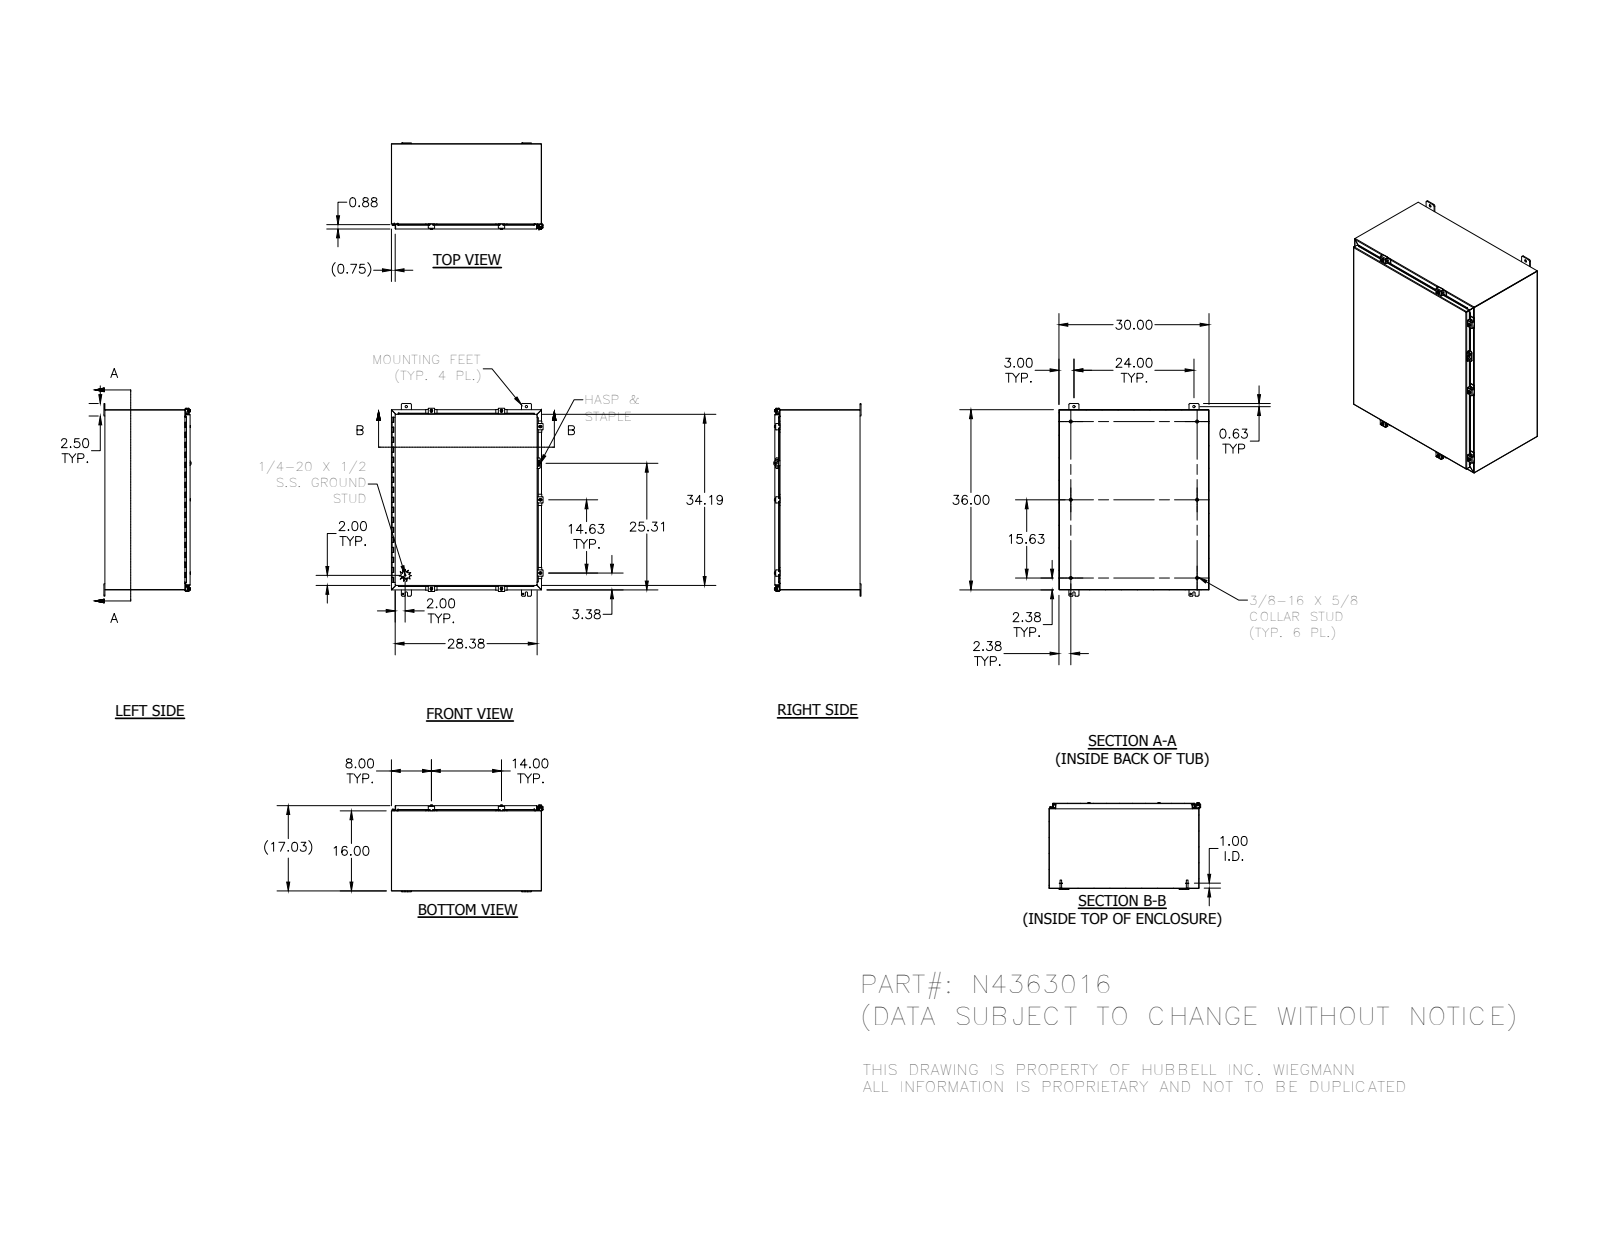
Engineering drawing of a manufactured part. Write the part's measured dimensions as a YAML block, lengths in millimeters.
part_name: "30824-1_1; 34840_1; 30823_1; 328134T_1 (+8 more)"
step_written_by: "SolidWorks 2014 (AUTOMOTIVE_DESIGN)"
units: millimeters
bodies: {solids: 56, faces: 2048, planar: 838, cylindrical: 887, other: 323}
overall_size: [977.9, 769.9, 442.2]
volume: 5932000
surface_area: 6185000
round_holes:
  - {diameter: 5.4, count: 7}
  - {diameter: 7.1, count: 7}
  - {diameter: 7.6, count: 7}
  - {diameter: 8, count: 4}
  - {diameter: 11.1, count: 4}
  - {diameter: 2.8, count: 3}
  - {diameter: 3.2, count: 1}
  - {diameter: 4, count: 1}
  - {diameter: 12.7, count: 1}
round_bosses_or_shafts:
  - {diameter: 6.4, count: 9}
  - {diameter: 13.2, count: 7}
  - {diameter: 12.7, count: 7}
  - {diameter: 8.9, count: 7}
  - {diameter: 15.9, count: 6}
  - {diameter: 8.4, count: 6}
  - {diameter: 2.9, count: 2}
  - {diameter: 8.6, count: 1}
partial_cylinders:
  - {radius: 0.8, count: 83}
  - {radius: 3.2, count: 37}
  - {radius: 6.4, count: 33}
  - {radius: 0.8, count: 21}
  - {radius: 2.7, count: 21}
  - {radius: 1.6, count: 19}
  - {radius: 3.6, count: 14}
  - {radius: 2.5, count: 10}
face_to_face_distances: [1.9, 430.8, 760.1, 428.9, 432.6, 912.5, 758.2, 762, 910.6, 914.4]
hole_center_spacings: [40.5, 609.6, 914.4, 1099, 20.1, 127.5, 128.7, 186.5]
